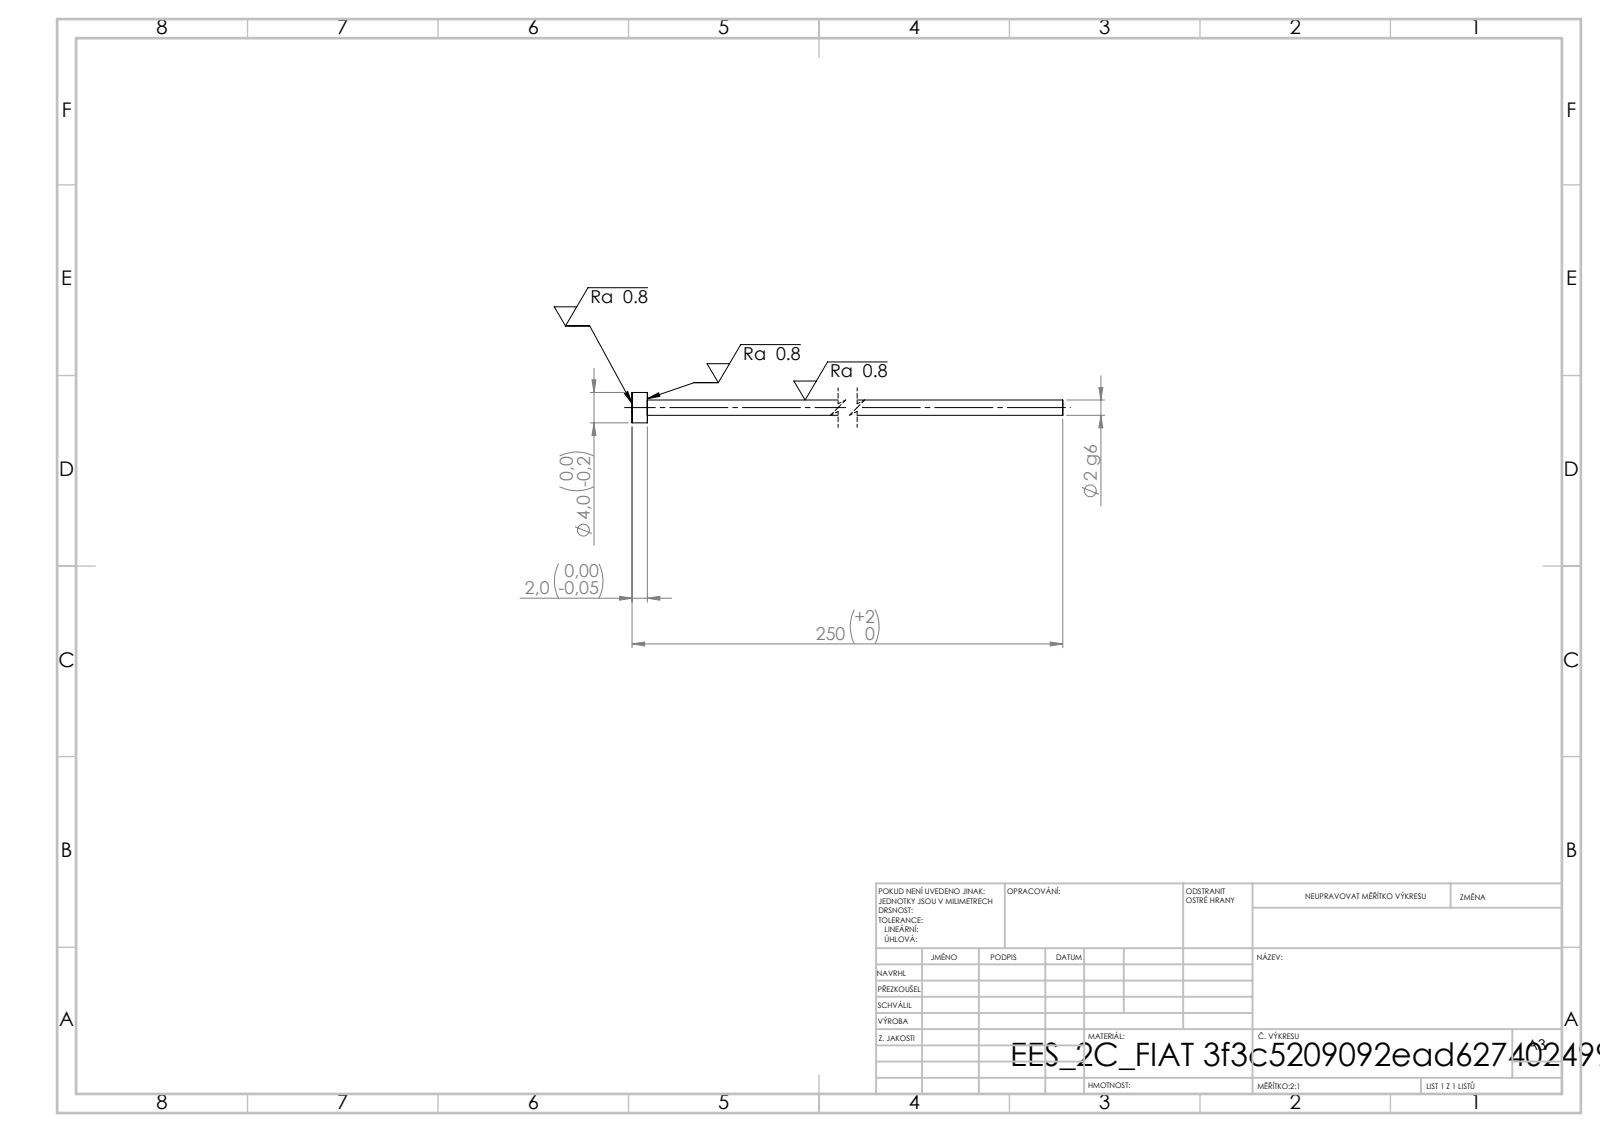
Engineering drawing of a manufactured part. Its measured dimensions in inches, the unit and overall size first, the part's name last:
Units: inches
Overall size (bounding box): 9.843 × 0.157 × 0.157
Round bosses / shafts (diameter × count): ⌀0.157 ×1, ⌀0.079 ×1
Main face-to-face distances: 0.079, 9.843, 9.764
Volume: 0.049 in³ · Surface area: 2.492 in²
Bodies: 1 solid, 7 faces (3 planar, 4 cylindrical, 0 other)
STEP written by: SolidWorks 2019 (CONFIG_CONTROL_DESIGN)
